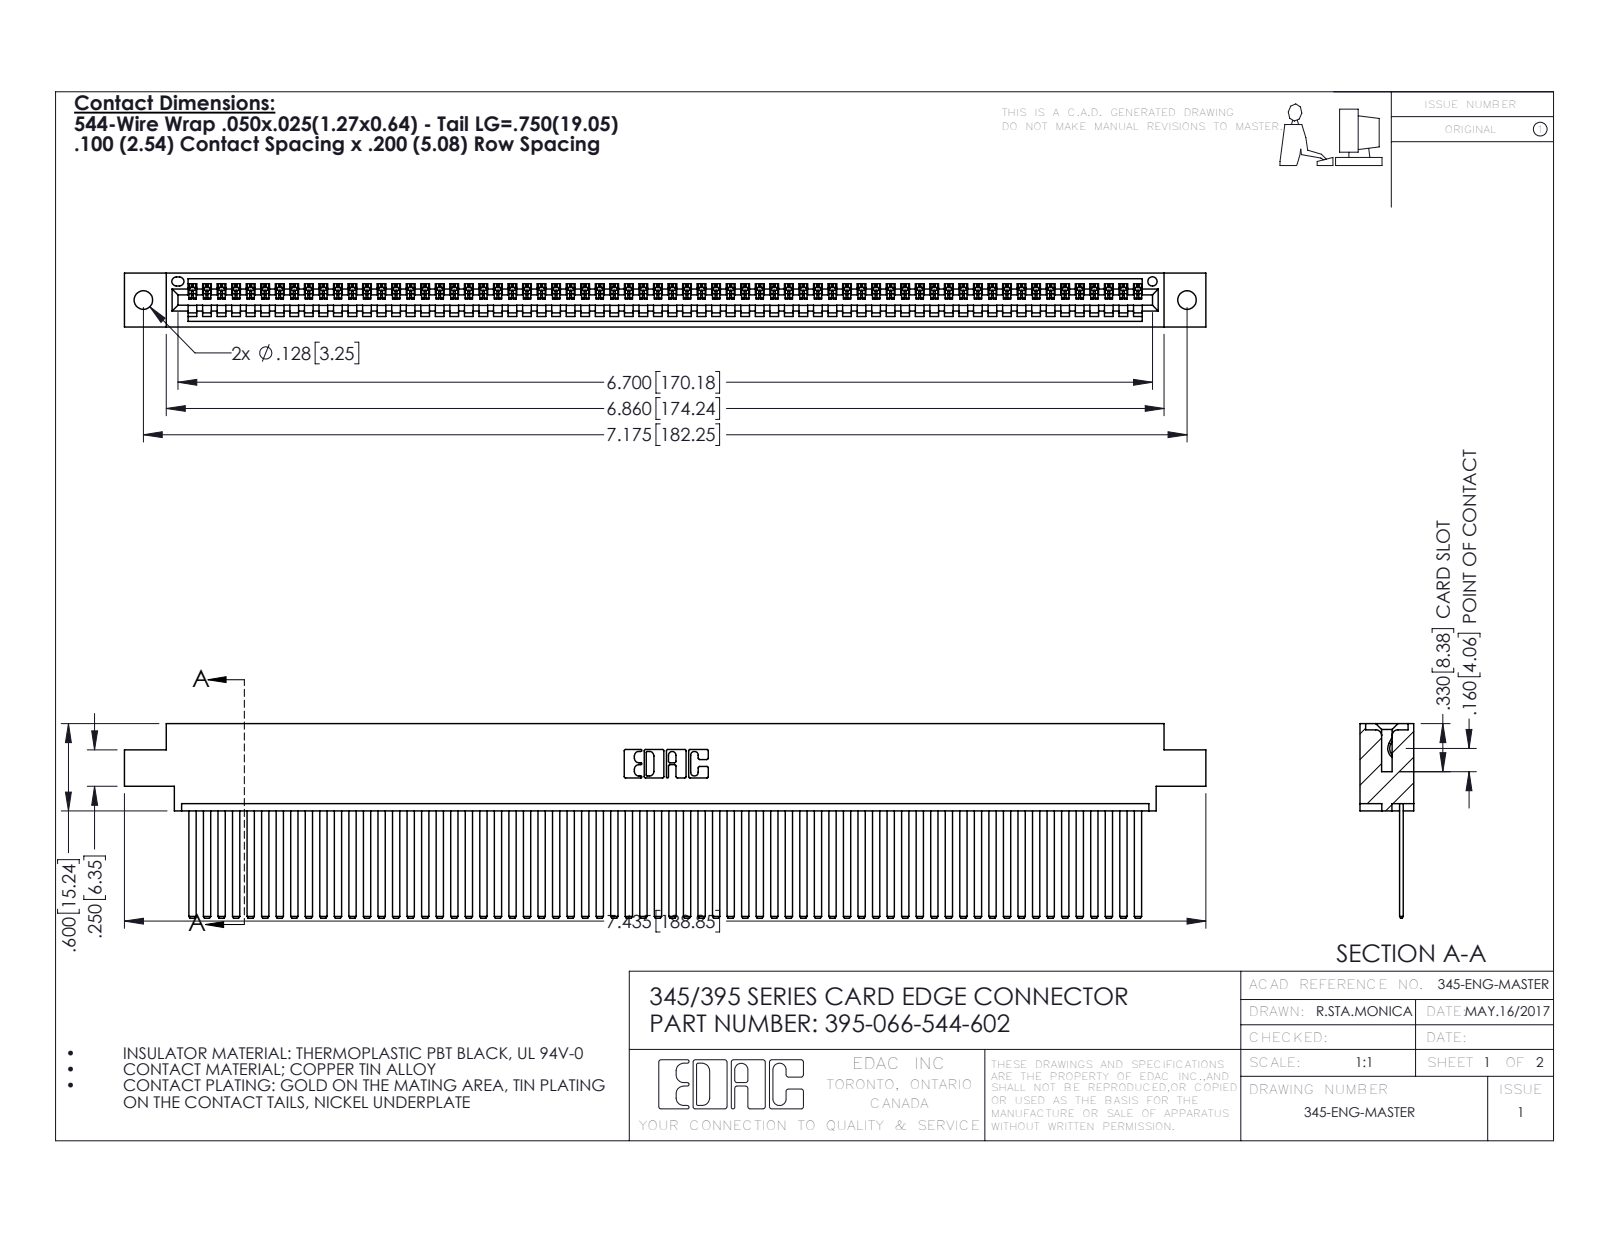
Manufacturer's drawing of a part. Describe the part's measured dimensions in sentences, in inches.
The part is named "395-066-544-602; 345 Part_0.170 Offset - 0.128 Dia; 345-292-001_345-293-144". Its 3-D file was written by "SolidWorks 2016 (CONFIG_CONTROL_DESIGN)". It is 67 solids with 3562 faces: 2460 planar, 1102 cylindrical and 0 other. Overall it measures 7.435 by 1.337 by 0.37 inches. Its volume is 1.144 cubic inches and its surface area 42.46 square inches. Round holes: 2 of diameter 0.128, 1 of diameter 0.064. Partial cylindrical surfaces (rounded edges, fillets, slot ends): 132 of radius 0.006, 22 of radius 0.01, 6 of radius 0.007, 6 of radius 0.031, 3 of radius 0.026, 2 of radius 0.031, 2 of radius 0.04, 1 of radius 0.014. The main face-to-face distances are 0.072, 0.298, 0.025, 0.098, 0.272, 0.37, 0.2, 0.225, 0.175, 0.149. The hole center spacings are 0.27, 6.939, 7.175.
